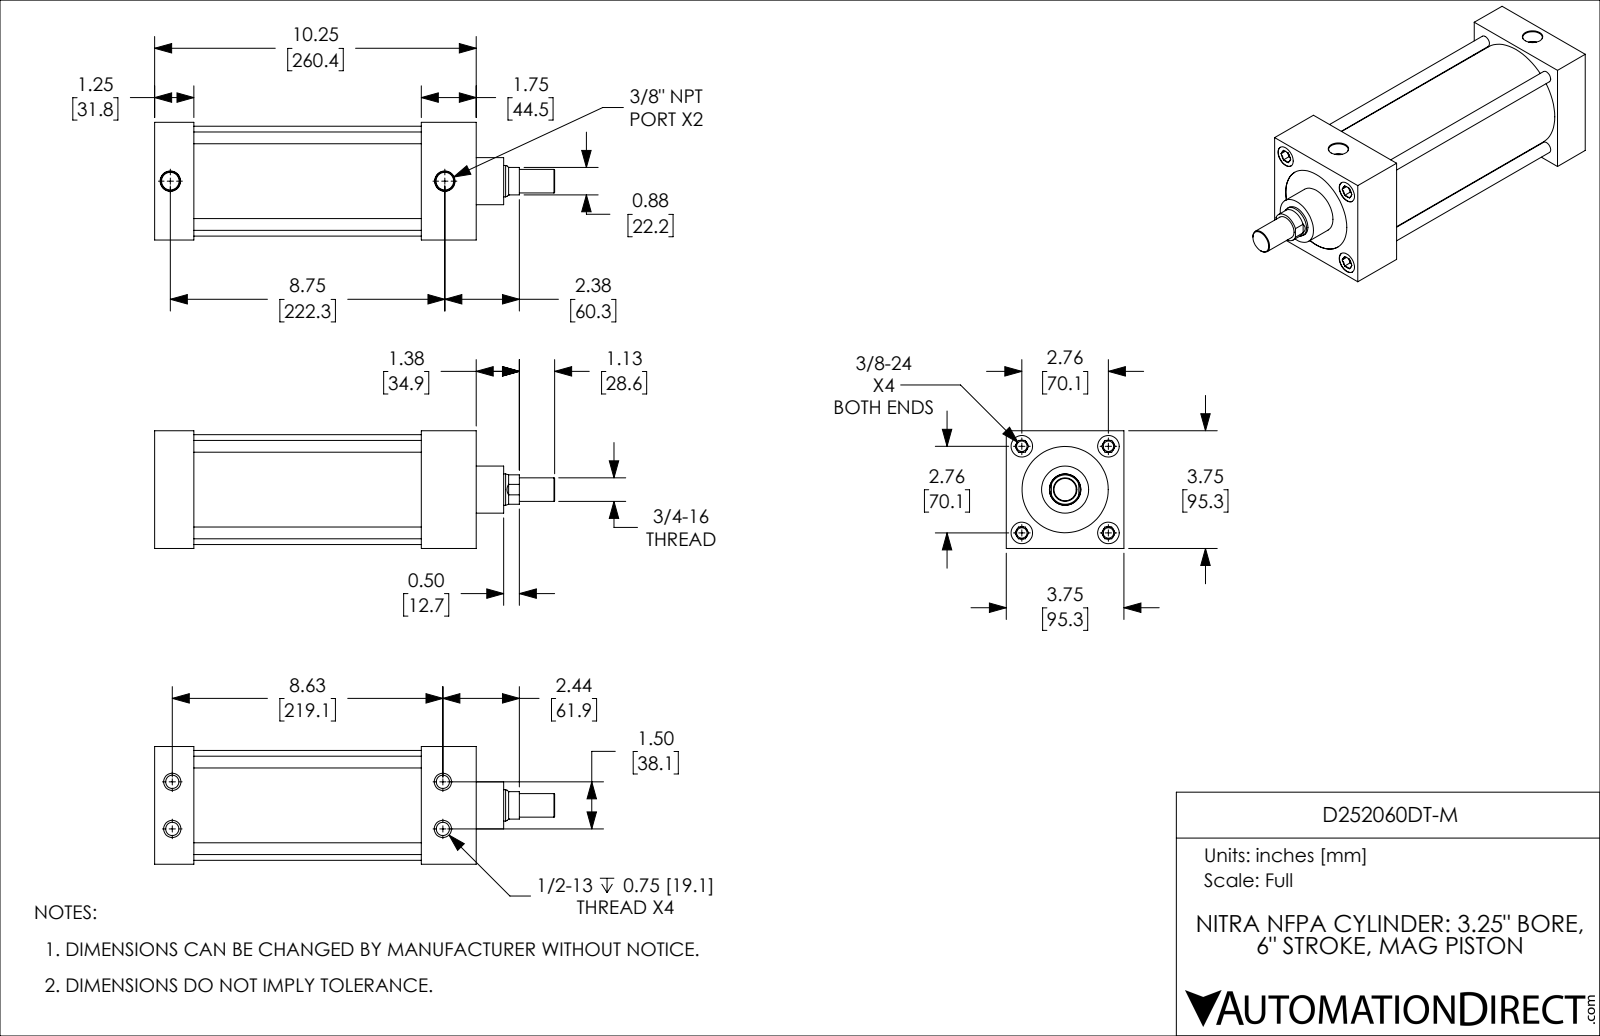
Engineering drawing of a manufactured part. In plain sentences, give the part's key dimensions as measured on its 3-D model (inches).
The part is named "D252060DT-M_BODY; D252060DT-M_PISTON_KK1; D252060DT-M". Its 3-D file was written by "SolidWorks 2019 (CONFIG_CONTROL_DESIGN)". It is 2 solids with 198 faces: 58 planar, 62 cylindrical and 78 other. Overall it measures 12.75 by 3.75 by 3.75 inches. Its volume is 70.25 cubic inches and its surface area 375.7 square inches. Round holes: 4 of diameter 0.332, 4 of diameter 0.422, 4 of diameter 0.687, 2 of diameter 0.562, 1 of diameter 1, 1 of diameter 2.75, 1 of diameter 3.251. Round bosses or shafts: 4 of diameter 0.375, 1 of diameter 3.501, 1 of diameter 3.249, 1 of diameter 1.5, 1 of diameter 0.999, 1 of diameter 0.75. Partial cylindrical surfaces (rounded edges, fillets, slot ends): 1 of radius 0.469. The main face-to-face distances are 1.25, 3.75, 8.5, 7.25, 2.5, 6, 10.25, 9, 7.75, 1.75. The hole center spacings are 0.753, 1.952, 2.76, 8.72, 1.5, 3.903, 8.625, 8.754.
